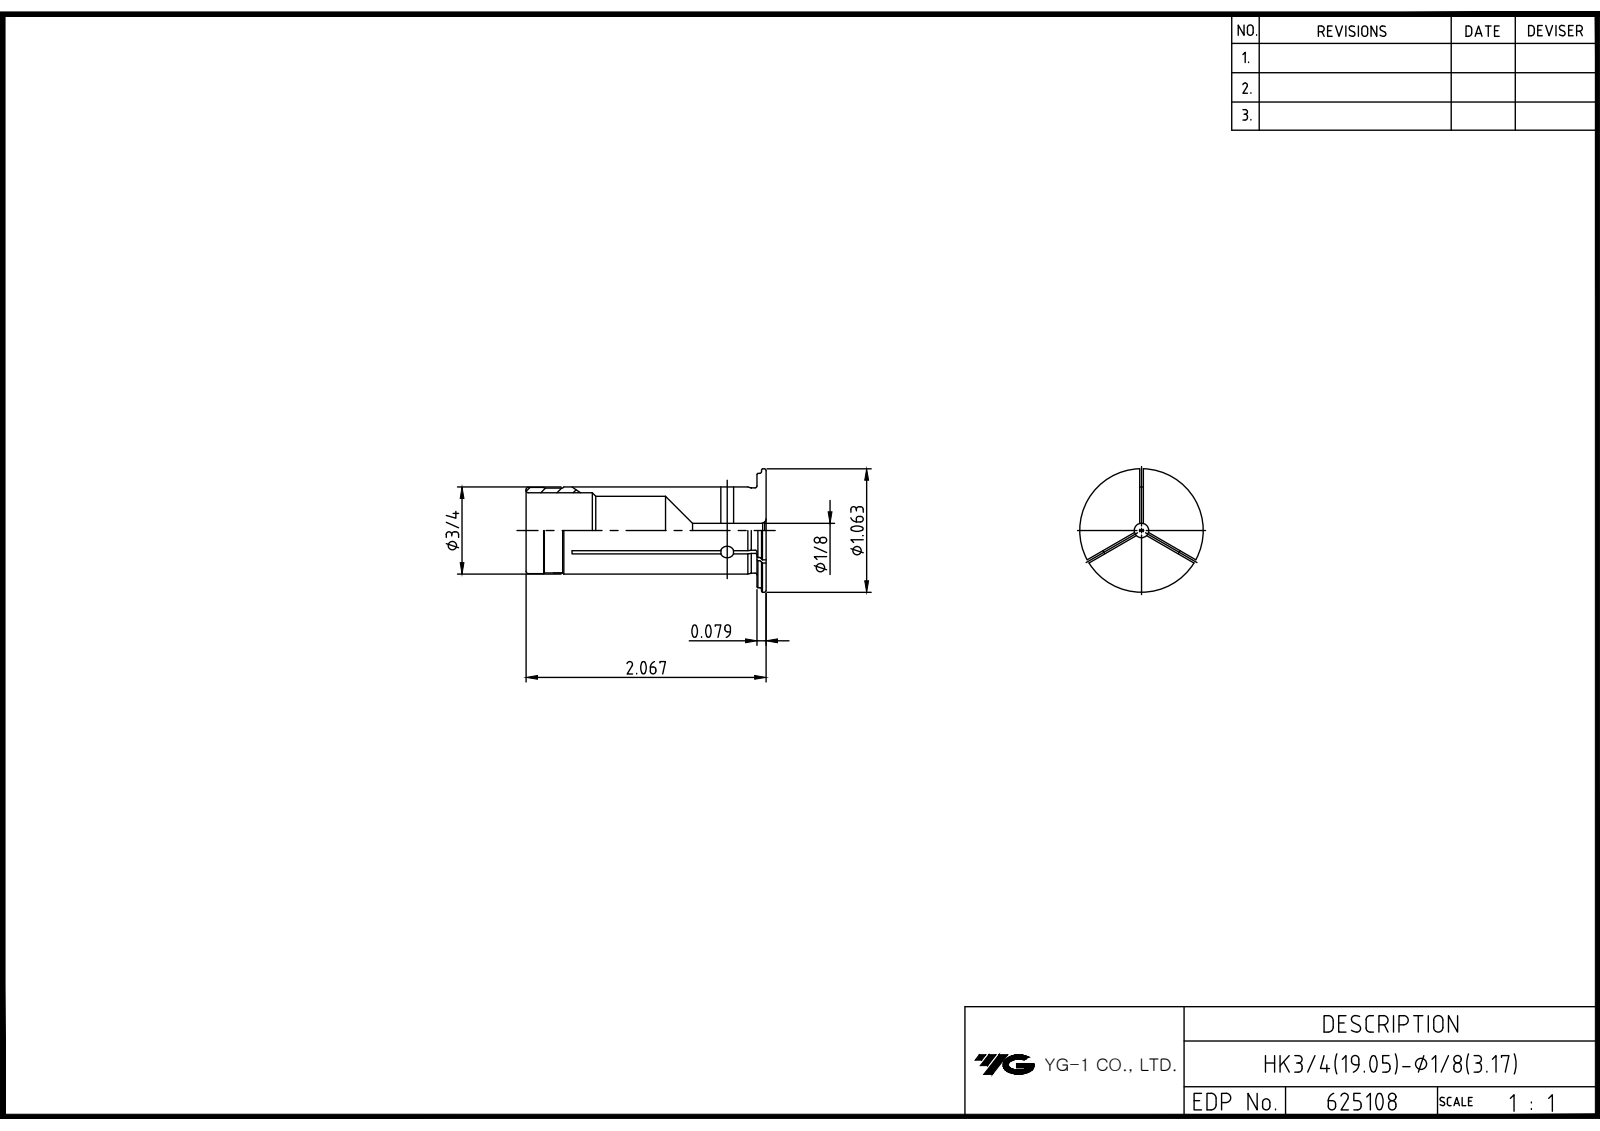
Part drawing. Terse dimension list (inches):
name: LO-HK19.05-3.175
written by: Autodesk Inventor 2022 (AUTOMOTIVE_DESIGN)
unit: in
bodies: 1 solid, 12 faces (4 planar, 6 cylindrical, 2 other)
size: 2.067 × 1.063 × 1.063
volume: 0.546 in³; area: 9.348 in²
holes: 1× ⌀0.125, 1× ⌀0.591, 1× ⌀0.65
bosses: 1× ⌀1.063, 1× ⌀0.984, 1× ⌀0.75
face distances: 0.079, 0.039, 1.988, 2.028, 2.067
